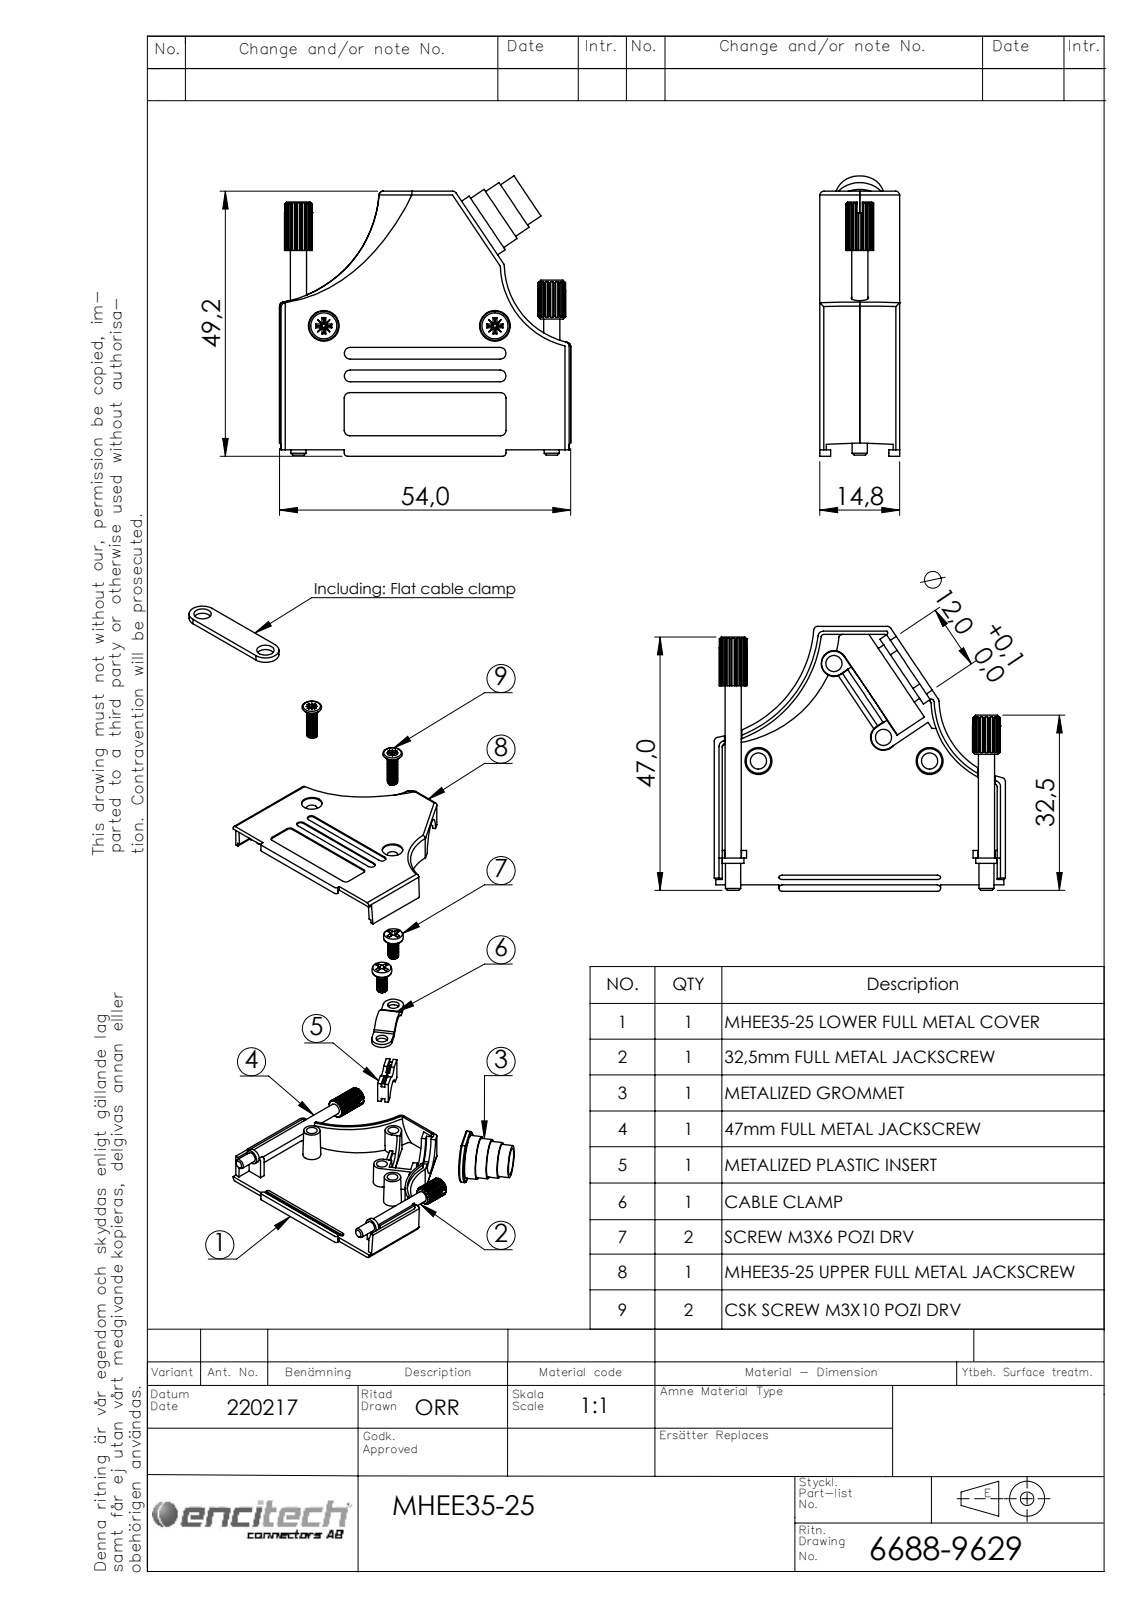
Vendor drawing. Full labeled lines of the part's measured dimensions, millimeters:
Part name (STEP PRODUCT): 6830-0109-01; 6855-0117-03; 6560-0140-13; 6805-0139-03 (+6 more)
STEP written by: SolidWorks 2021 (AUTOMOTIVE_DESIGN)
Units: millimetres
Bodies: 11 solids, 854 faces (412 planar, 314 cylindrical, 128 other)
Overall size (bounding box): 54 × 52.05 × 14.8
Volume: 9 052 mm³ · Surface area: 16 021 mm²
Round holes (diameter × count): ⌀3 ×4, ⌀3.2 ×4, ⌀4.8 ×2, ⌀5.7 ×2, ⌀7.5 ×1, ⌀8.5 ×1, ⌀9.5 ×1, ⌀10.5 ×1, ⌀12 ×1
Round bosses / shafts (diameter × count): ⌀2.9 ×4, ⌀4 ×2, ⌀3 ×2, ⌀2.8 ×2, ⌀11 ×1, ⌀10 ×1, ⌀9 ×1
Partial cylindrical surfaces — rounded edges, fillets, slot ends (radius × count): R0.75 ×10, R1 ×9, R0.1 ×8, R0.3 ×7, R1.1 ×4, R0.38 ×3, R0.5 ×3, R0.6 ×2
Main face-to-face distances: 1.2, 13.6, 12.4, 14.8, 14.5, 6.2, 0.9, 13.3, 7.4, 7.1
Hole centre spacings: 9.61, 16.5, 22.87, 23.61, 25.34, 31.75, 47
